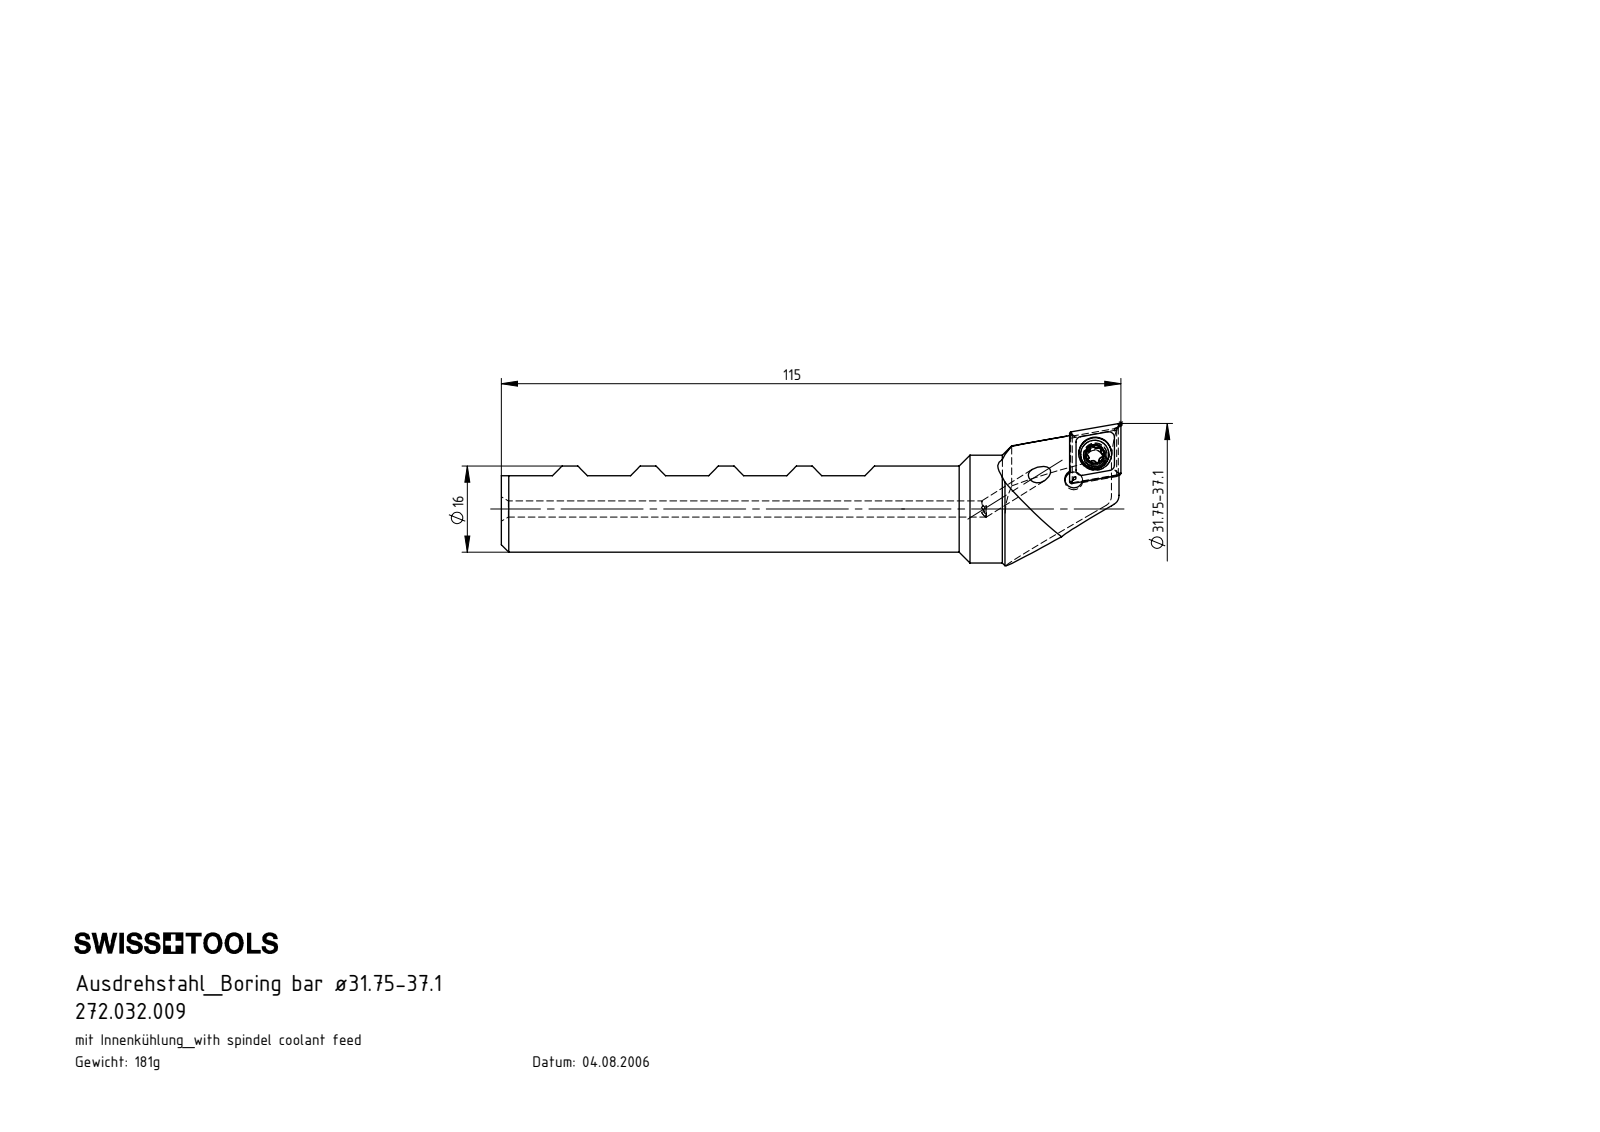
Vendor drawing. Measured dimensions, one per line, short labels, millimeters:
name: B32-WCB.K11.115; WCB-ER2.001.009_A; CCMT09T304; B32-WCB.K11.115_A
written by: SolidWorks 2012 (CONFIG_CONTROL_DESIGN)
unit: mm
bodies: 3 solids, 146 faces (45 planar, 40 cylindrical, 61 other)
size: 115 × 26.38 × 21.89
volume: 23 044 mm³; area: 7 981 mm²
holes: 2× ⌀3, 2× ⌀3.3, 1× ⌀4.4, 1× ⌀6.1
bosses: 1× ⌀20, 1× ⌀16, 1× ⌀5.25, 1× ⌀4
rounds: 6× R0.34, 6× R0.59, 1× R2, 1× R10.5, 1× R12
face distances: 7.91, 10.25, 20.5, 30.76, 20.51, 11.68, 3.77, 11.88, 3.97, 30.75
hole spacings: 6.07, 6.2
